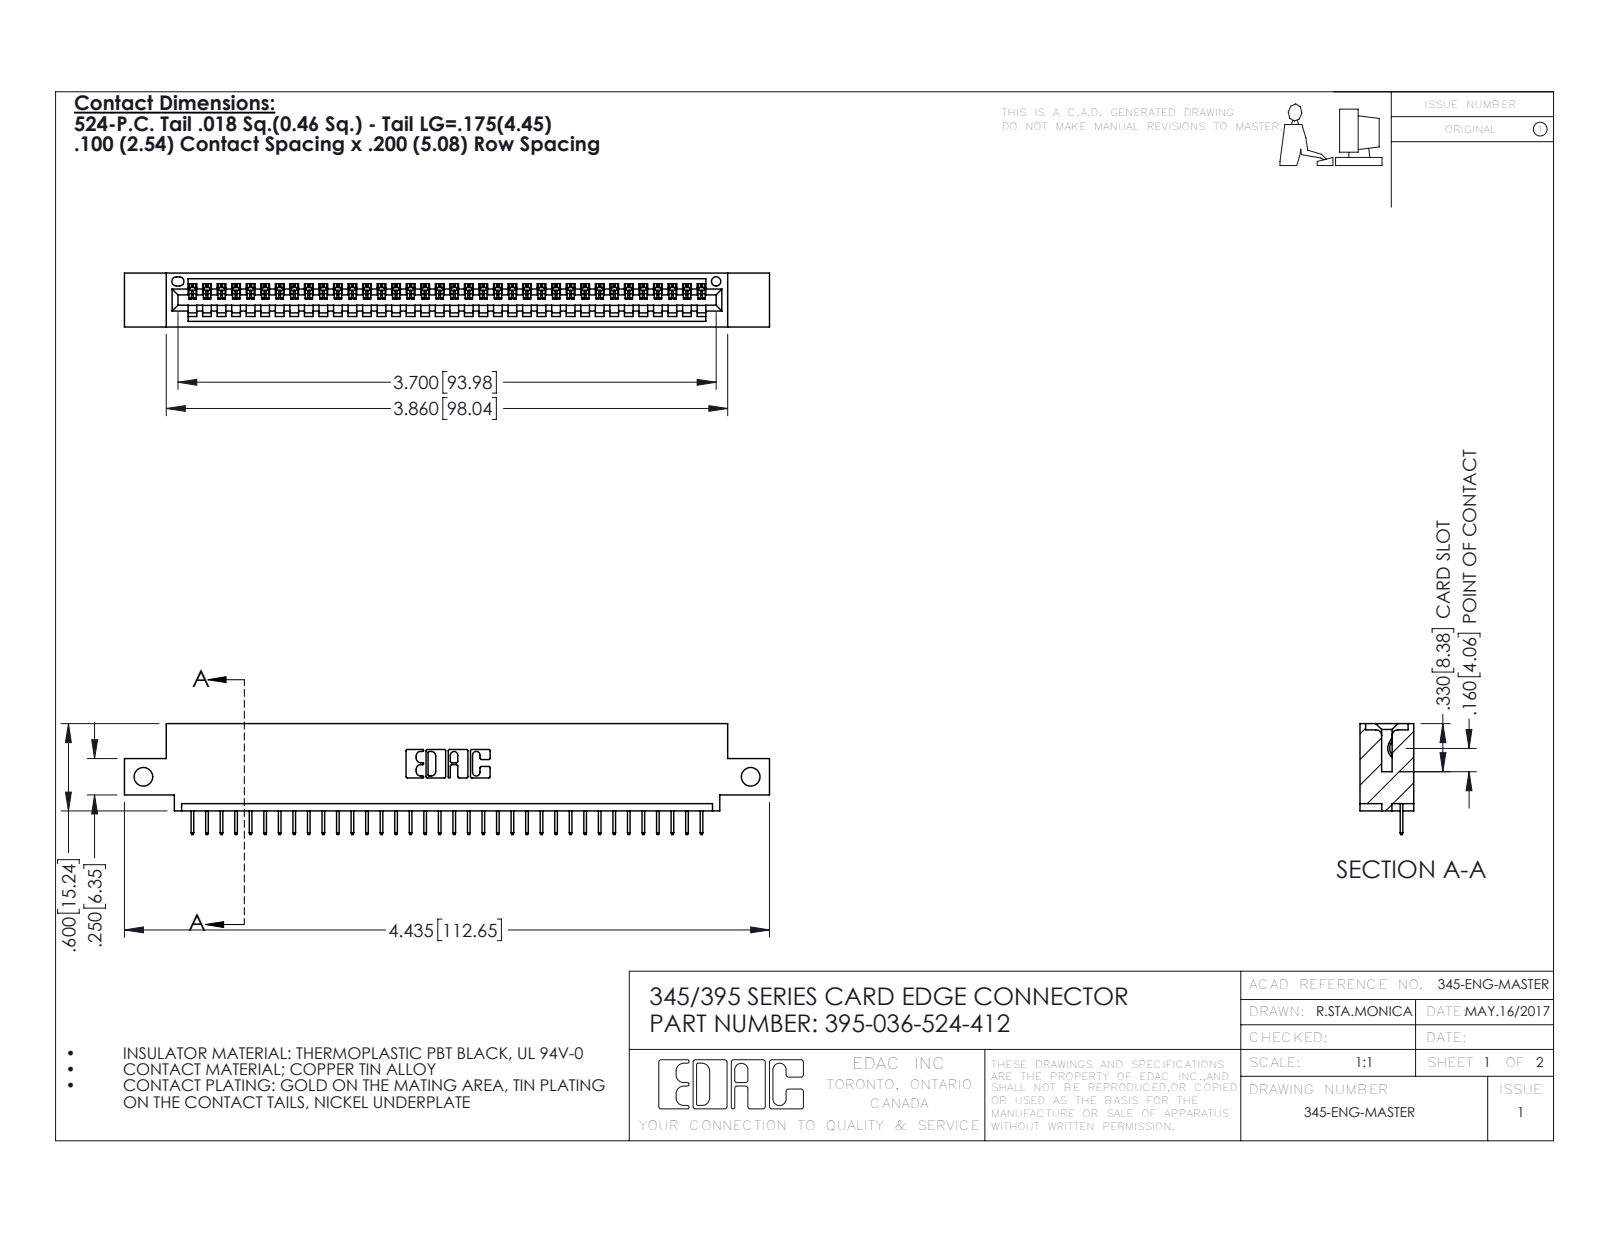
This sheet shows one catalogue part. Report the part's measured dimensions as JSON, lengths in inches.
{"part_name": "395-036-524-412; 345 Part_0.110 Offset - Side Mount; 345-292-001_345-293-124", "step_written_by": "SolidWorks 2016 (CONFIG_CONTROL_DESIGN)", "units": "inches", "bodies": {"solids": 37, "faces": 2362, "planar": 1740, "cylindrical": 622, "other": 0}, "overall_size": [4.435, 0.762, 0.37], "volume_in3": 0.631, "surface_area_in2": 20.39, "round_holes": [[0.128, 2], [0.064, 1]], "partial_cylinders_radius": [[0.006, 72], [0.01, 22], [0.007, 6], [0.031, 6], [0.026, 3], [0.031, 2], [0.04, 2], [0.014, 1]], "face_to_face_distances": [0.072, 0.298, 0.37, 0.2, 0.098, 0.272, 0.025, 0.225, 0.072, 0.149], "hole_center_spacings": [4.175]}
